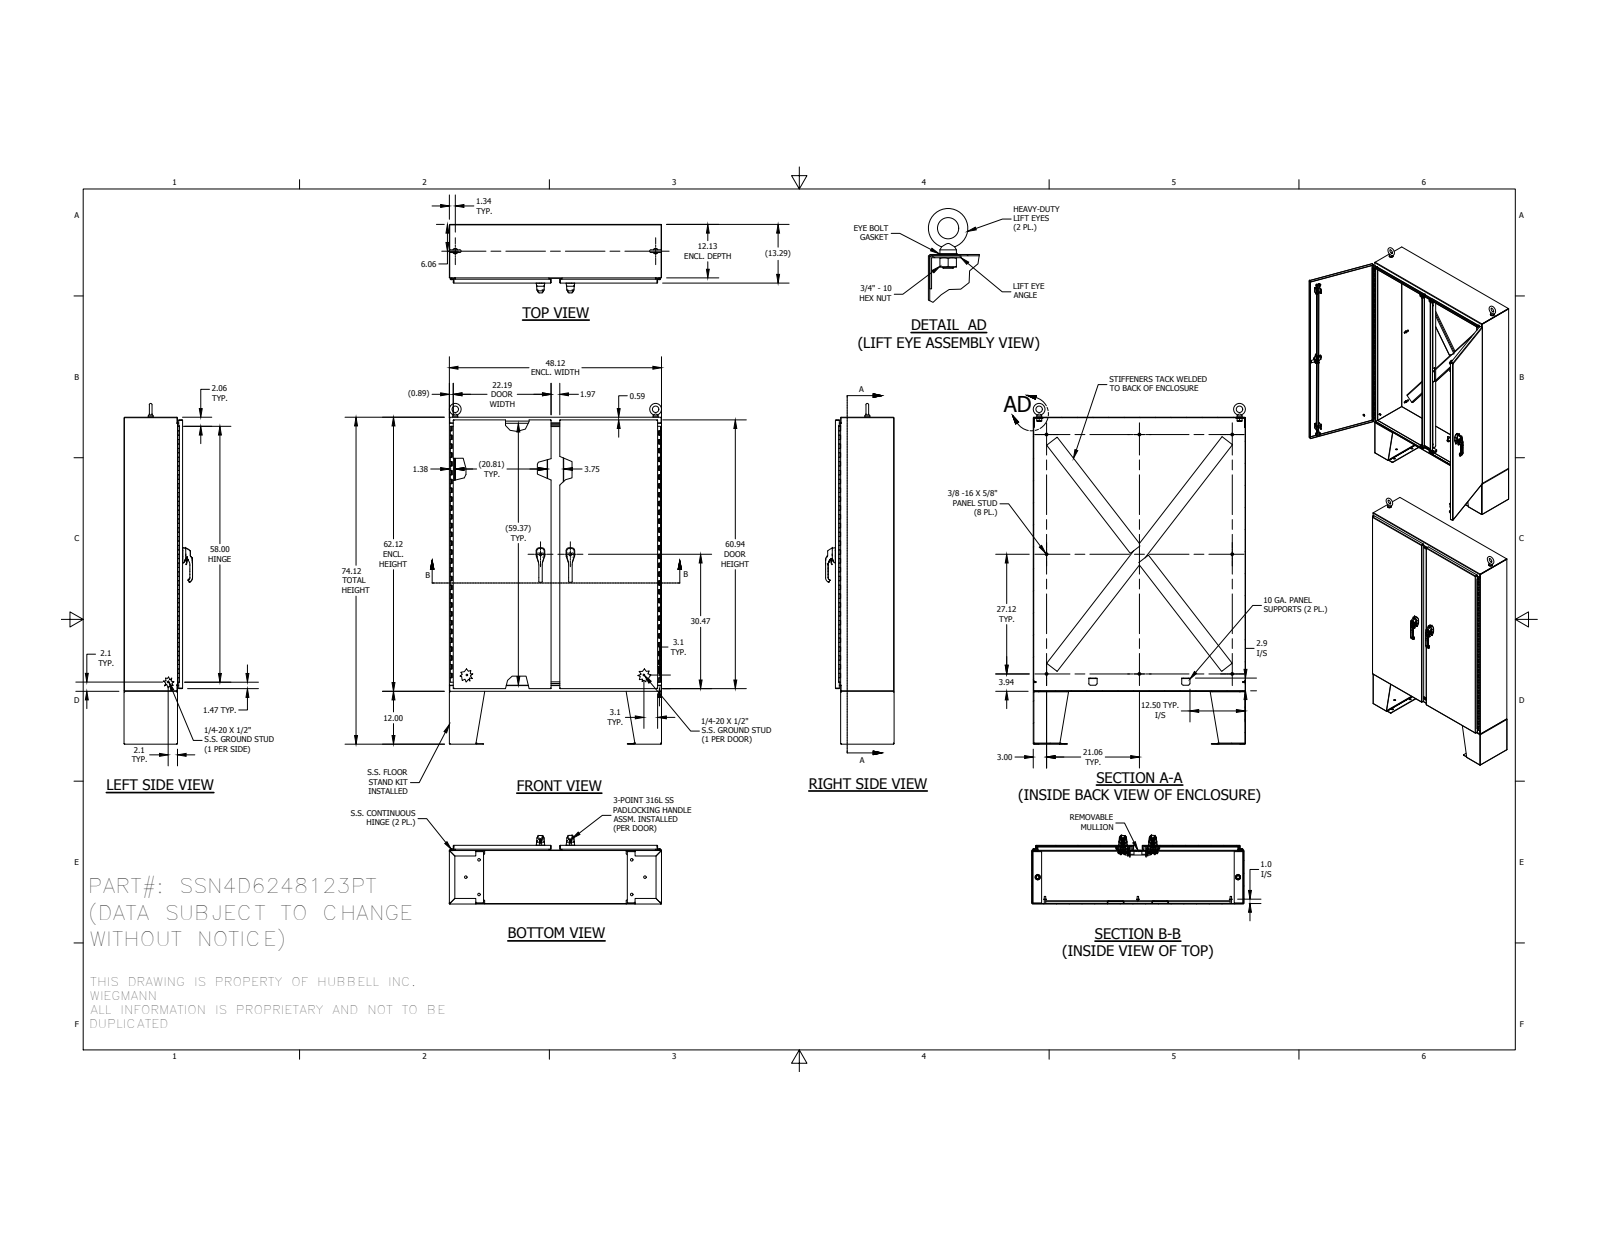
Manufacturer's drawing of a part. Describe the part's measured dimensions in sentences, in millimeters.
The part is named "D125B_10_5_1; SSN4D62483PTLDR_1; HFW3762_1; LOCK-NUT_AF0_1 (+8 more)". Its 3-D file was written by "SolidWorks 2014 (AUTOMOTIVE_DESIGN)". It is 138 solids with 7184 faces: 2696 planar, 2772 cylindrical and 1716 other. Overall it measures 1962.1 by 1222.4 by 394.7 millimeters. Its volume is 19 030 000 cubic millimeters and its surface area 15 580 000 square millimeters. Round holes: 18 of diameter 14.3, 16 of diameter 6.7, 16 of diameter 9.5, 8 of diameter 4.7, 6 of diameter 5.4, 6 of diameter 7.1, 5 of diameter 6.4, 4 of diameter 5, 4 of diameter 6.1, 4 of diameter 6.4, 4 of diameter 7.1, 4 of diameter 8. Round bosses or shafts: 10 of diameter 8.4, 8 of diameter 15.9, 7 of diameter 6.4, 6 of diameter 13.5, 6 of diameter 6, 5 of diameter 25.4, 4 of diameter 14.3, 4 of diameter 13.5. Partial cylindrical surfaces (rounded edges, fillets, slot ends): 342 of radius 0.5, 213 of radius 0.3, 46 of radius 3.2, 42 of radius 0.5, 34 of radius 1.3, 32 of radius 0.8, 28 of radius 2, 24 of radius 0.6. The main face-to-face distances are 2.4, 335.2, 335.1, 1220, 332.8, 332.7, 337.6, 2.4, 337.5, 2.3. The hole center spacings are 163.7, 9.7, 9.7, 19.3, 327.4, 1176.6, 1322.1, 1331.6.
